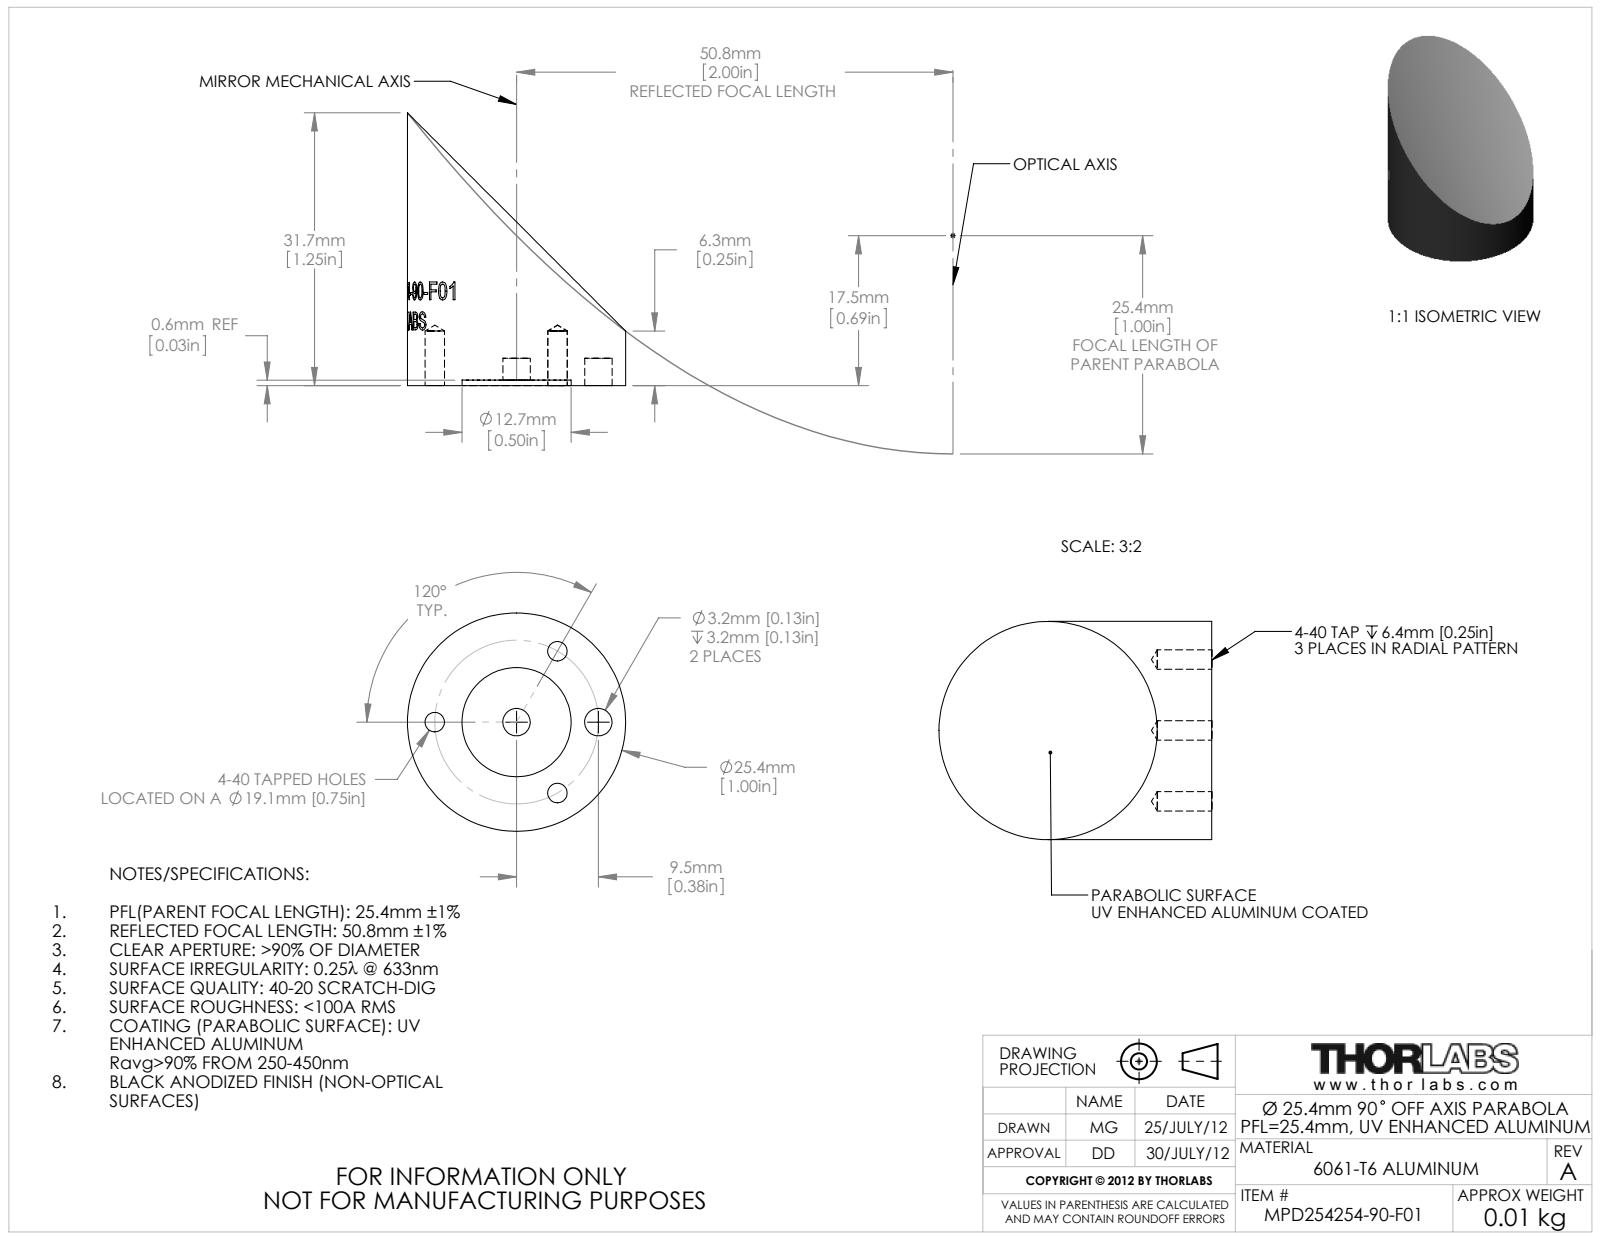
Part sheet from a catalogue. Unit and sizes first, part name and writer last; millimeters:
Units: millimetres
Overall size (bounding box): 31.75 × 25.4 × 25.4
Round holes (diameter × count): ⌀2.26 ×3, ⌀3.19 ×2, ⌀12.7 ×1
Round bosses / shafts (diameter × count): ⌀25.4 ×1
Main face-to-face distances: 0.64, 3.17, 2.53
Hole centre spacings: 9.52, 16.5, 9.53, 19.05
Volume: 9 044 mm³ · Surface area: 2 967 mm²
Bodies: 1 solid, 62 faces (4 planar, 50 cylindrical, 8 other)
Part name (STEP PRODUCT): 24688-E0W
STEP written by: SolidWorks 2012 (CONFIG_CONTROL_DESIGN)
